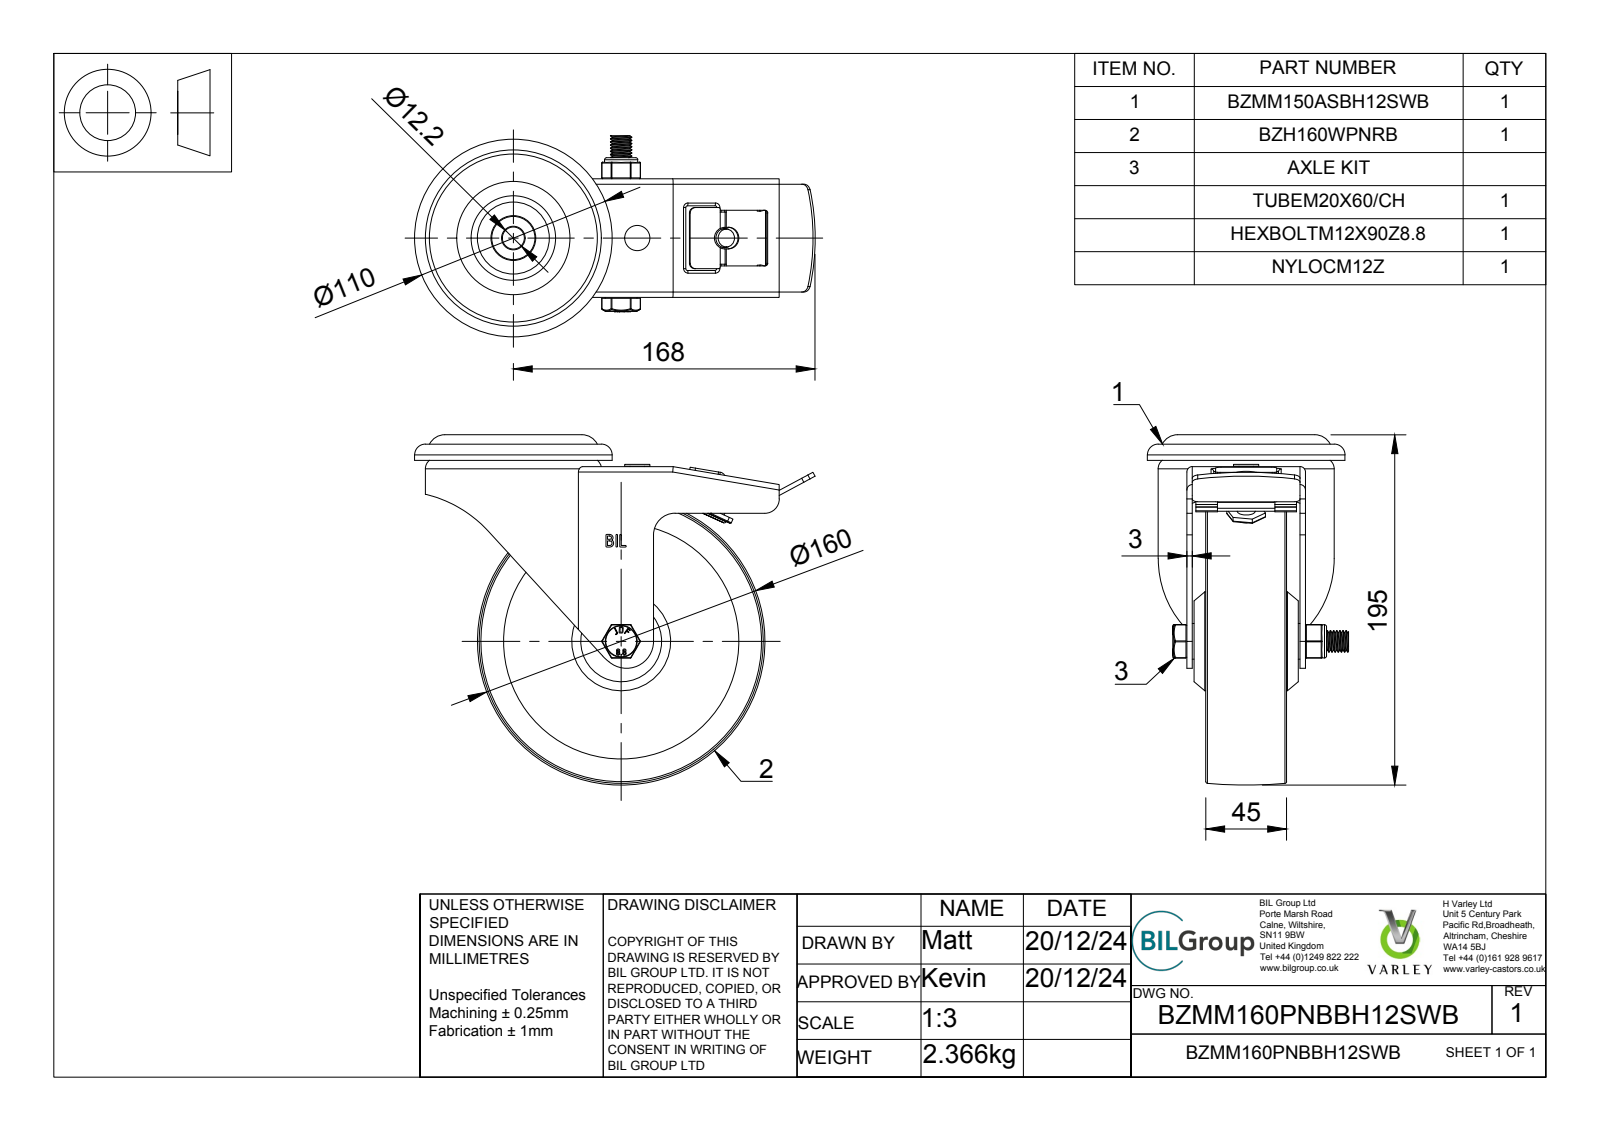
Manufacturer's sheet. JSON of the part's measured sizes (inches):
{"part_name": "BZMM160PNBBH12SWB v3; BZMM150ASBH12SWB v1; ZINC PLATED, PRESSED STEEL TOP PLATE; ZINC PLATED, PRESSED STEEL FORKS (+8 more)", "step_written_by": "Autodesk Translation Framework v13.20.0.188 (AP242_MANAGED_MODEL_BASED_3D_ENGINEERING_MIM_LF)", "units": "inches", "bodies": {"solids": 25, "faces": 713, "planar": 371, "cylindrical": 226, "other": 116}, "overall_size": [8.78, 7.677, 4.409], "volume_in3": 44.68, "surface_area_in2": 436.8, "round_holes": [[0.315, 2], [0.472, 1], [0.476, 1], [0.48, 1], [0.492, 1], [0.551, 1], [0.807, 1], [1.181, 1], [1.299, 1], [1.319, 1], [1.339, 1], [2.067, 1]], "round_bosses_or_shafts": [[0.197, 10], [4.331, 1], [3.031, 1], [2.165, 1], [1.575, 1], [1.295, 1], [1.161, 1], [0.984, 1]], "partial_cylinders_radius": [[0.02, 26], [0.059, 12], [0.118, 8], [0.039, 6], [0.019, 4], [0.035, 4], [0.079, 3], [0.098, 3]], "face_to_face_distances": [0.118, 0.413, 2.067, 1.535, 0.472, 0.295, 0.65, 1.063, 1.122, 2.185], "hole_center_spacings": [2.717]}
